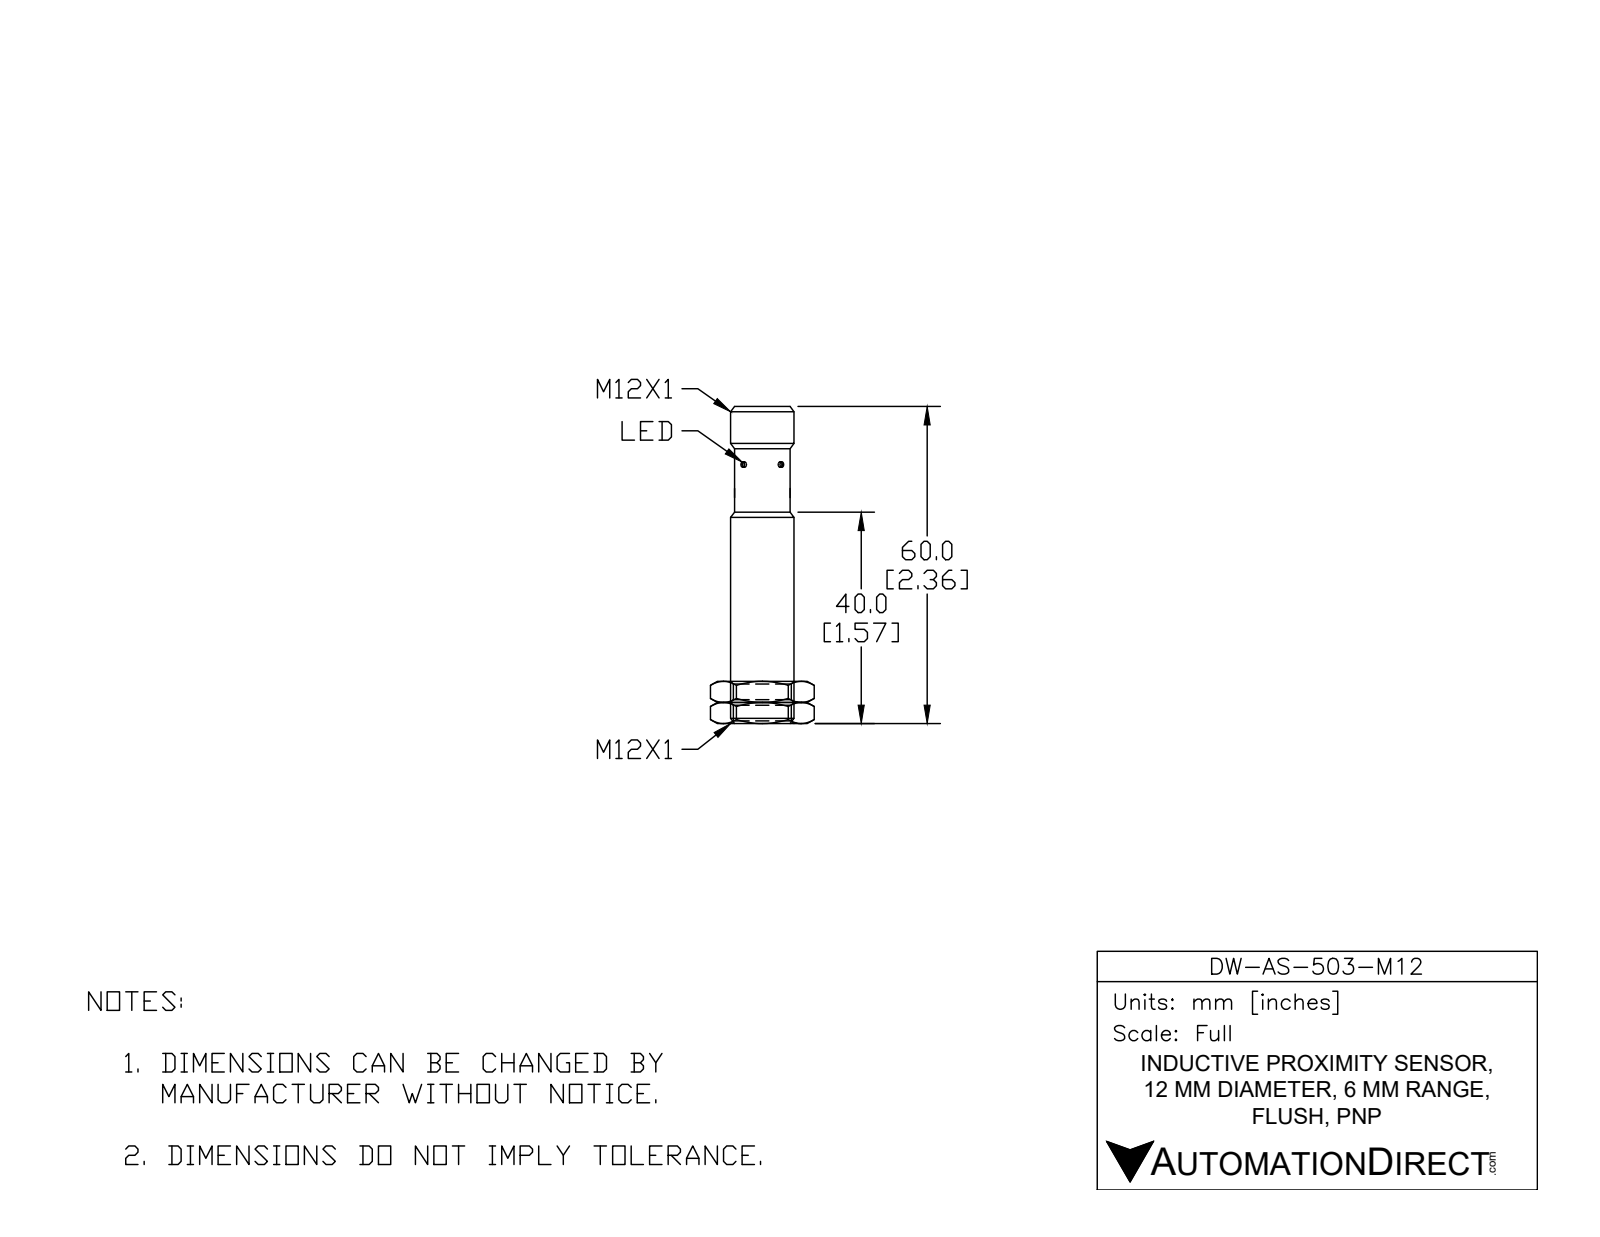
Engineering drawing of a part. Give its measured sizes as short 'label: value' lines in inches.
name: DW-AS-503-M12
written by: SolidWorks 2017 (AUTOMOTIVE_DESIGN)
unit: in
bodies: 1 solid, 35 faces (7 planar, 19 cylindrical, 9 other)
size: 2.362 × 0.472 × 0.472
volume: 0.367 in³; area: 4.348 in²
holes: 2× ⌀0.118, 1× ⌀0.335
bosses: 4× ⌀0.039, 1× ⌀0.472, 1× ⌀0.415
rounds: 2× R0.022, 1× R0.193
face distances: 2.02, 2.362, 0.343, 0.043, 1.614, 0.406, 0.748, 2.047, 0.433, 0.028
